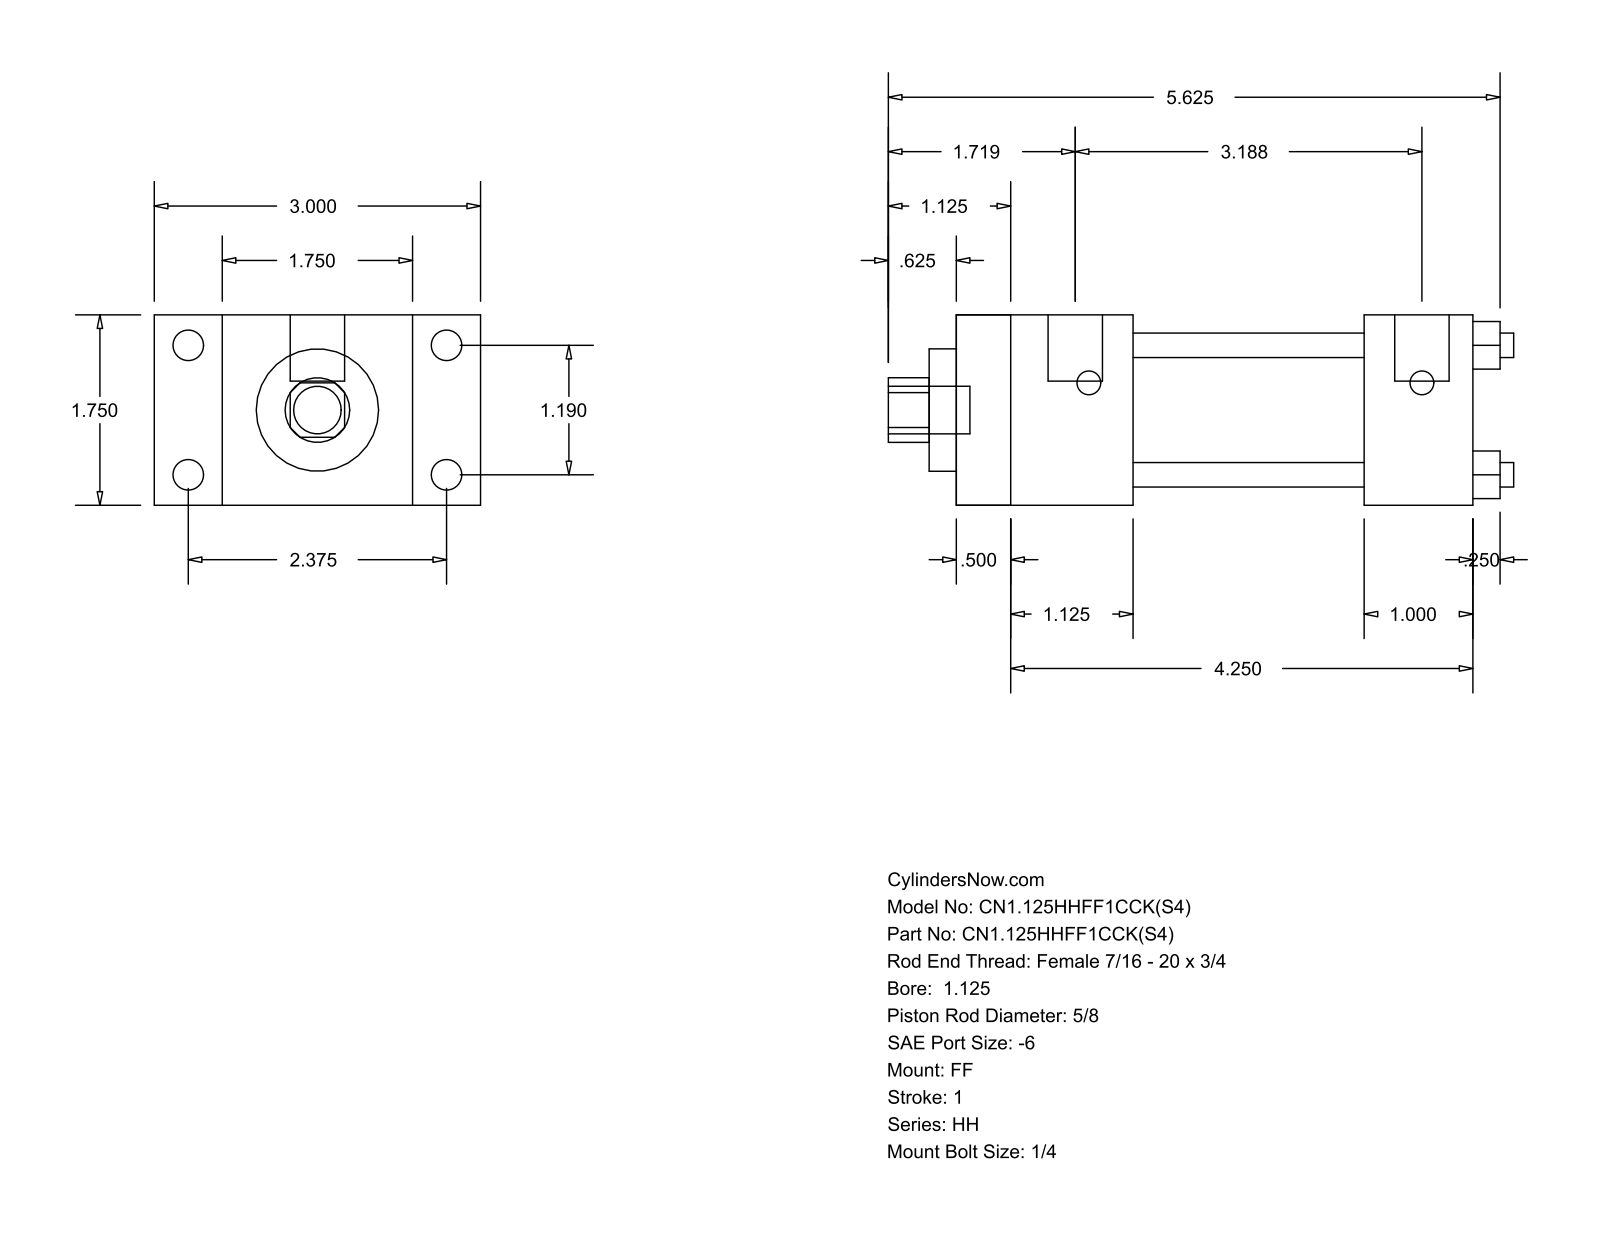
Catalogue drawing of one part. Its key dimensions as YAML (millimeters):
part_name: "HH_FF__0112_0.625"
step_written_by: "GSSL Pune (CONFIG_CONTROL_DESIGN)"
units: millimeters
bodies: {solids: 0, faces: 92, planar: 64, cylindrical: 28, other: 0}
overall_size: [146.05, 76.2, 44.45]
round_holes:
  - {diameter: 5.71, count: 4}
  - {diameter: 15.88, count: 1}
  - {diameter: 28.57, count: 1}
  - {diameter: 34.92, count: 1}
round_bosses_or_shafts:
  - {diameter: 7.14, count: 4}
  - {diameter: 5.56, count: 4}
  - {diameter: 12.7, count: 2}
  - {diameter: 11.11, count: 1}
partial_cylinders:
  - {radius: 7.54, count: 1}
face_to_face_distances: [44.46, 120.65, 12.69, 107.96, 15.87, 60.33, 28.58, 41.27, 95.24, 82.55]
hole_center_spacings: [21.37, 30.22, 42.74]
